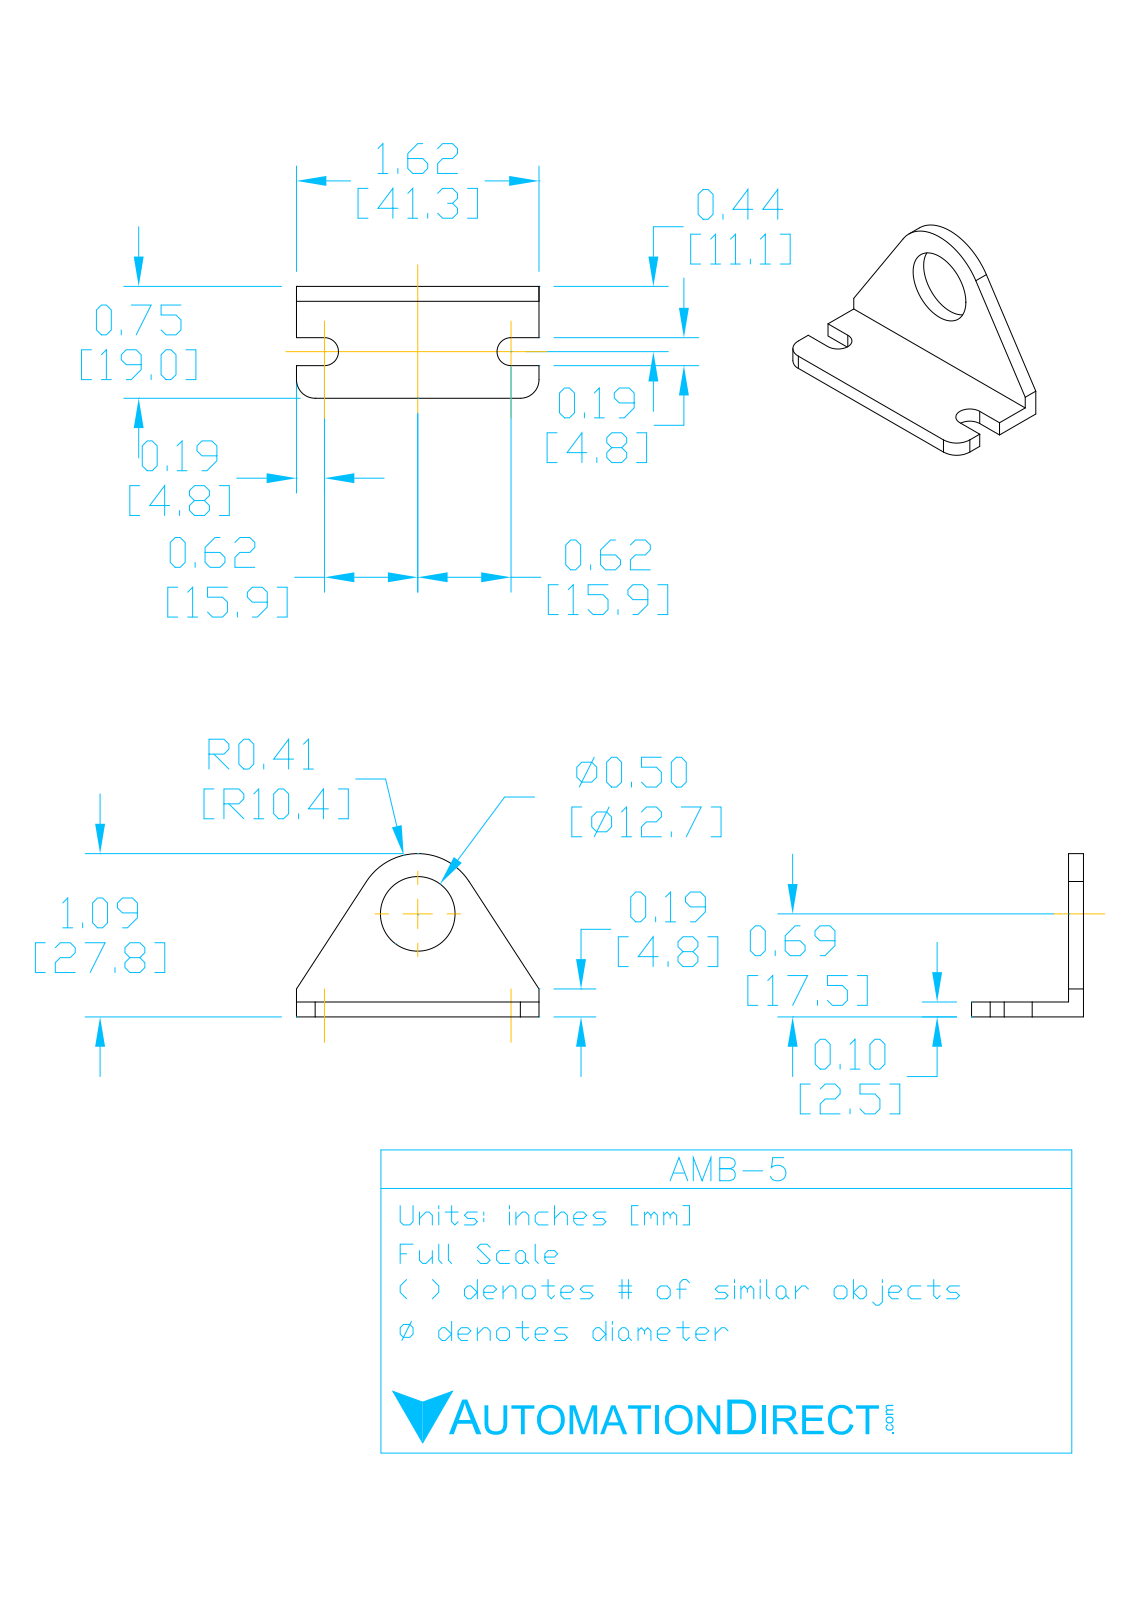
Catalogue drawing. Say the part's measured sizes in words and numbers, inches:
The part is named "AMB-5". Its 3-D file was written by "SolidWorks 2017 (AUTOMOTIVE_DESIGN)". It is 1 solid with 28 faces: 19 planar, 9 cylindrical and 0 other. Overall it measures 1.626 by 1.094 by 0.75 inches. Its volume is 0.189 cubic inches and its surface area 4.648 square inches. Round holes: 1 of diameter 0.5. Partial cylindrical surfaces (rounded edges, fillets, slot ends): 2 of radius 0.094, 2 of radius 0.187, 1 of radius 0.03, 1 of radius 0.128, 1 of radius 0.41. The main face-to-face distances are 0.098, 0.652, 0.75, 1.626, 0.218, 0.433, 0.532, 0.407, 0.189, 0.244.
